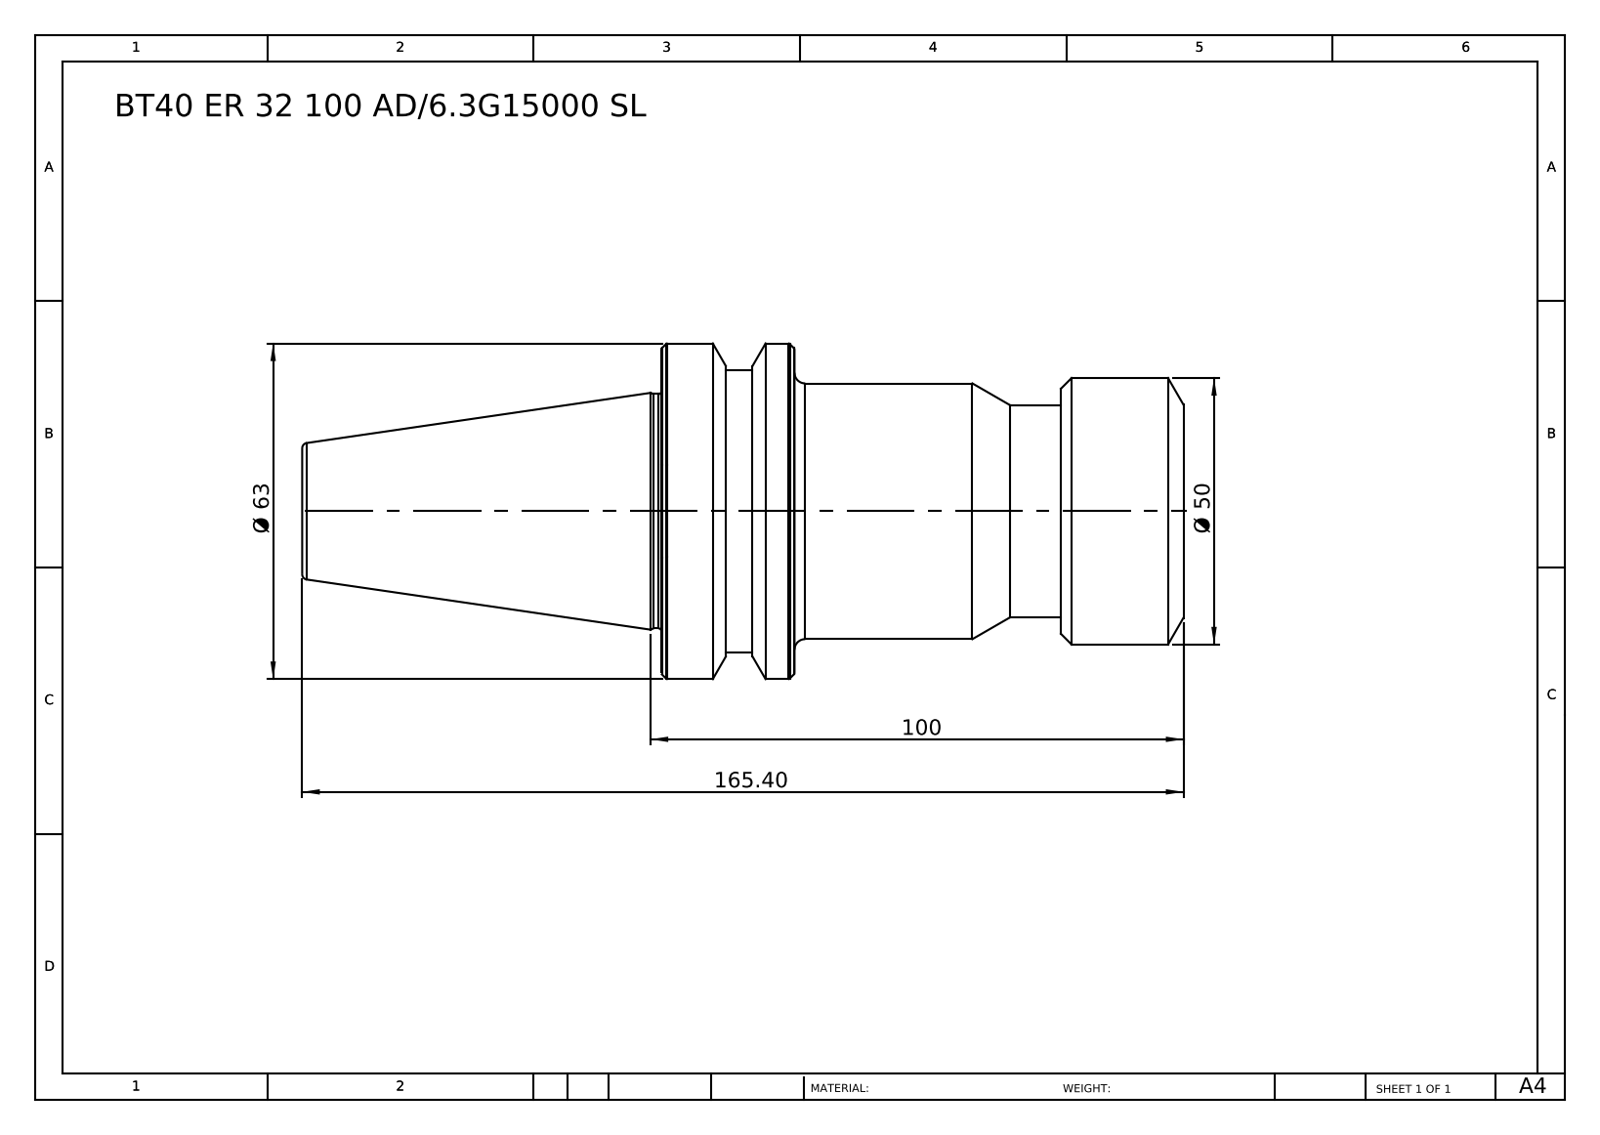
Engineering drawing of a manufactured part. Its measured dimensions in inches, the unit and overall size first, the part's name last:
Units: inches
Overall size (bounding box): 6.512 × 2.48 × 2.48
Round bosses / shafts (diameter × count): ⌀2.48 ×1, ⌀2.087 ×1, ⌀1.969 ×1, ⌀1.89 ×1, ⌀1.732 ×1, ⌀1.571 ×1
Main face-to-face distances: 3.858, 2.874, 0.984, 6.512, 3.638, 2.654, 0.906, 1.969, 2.953, 5.606
Volume: 16.2 in³ · Surface area: 45.74 in²
Bodies: 1 solid, 62 faces (7 planar, 14 cylindrical, 41 other)
Part name (STEP PRODUCT): BT40 ER 32 100 AD-6.3G15000 SL
STEP written by: SolidWorks 2014 (CONFIG_CONTROL_DESIGN)
